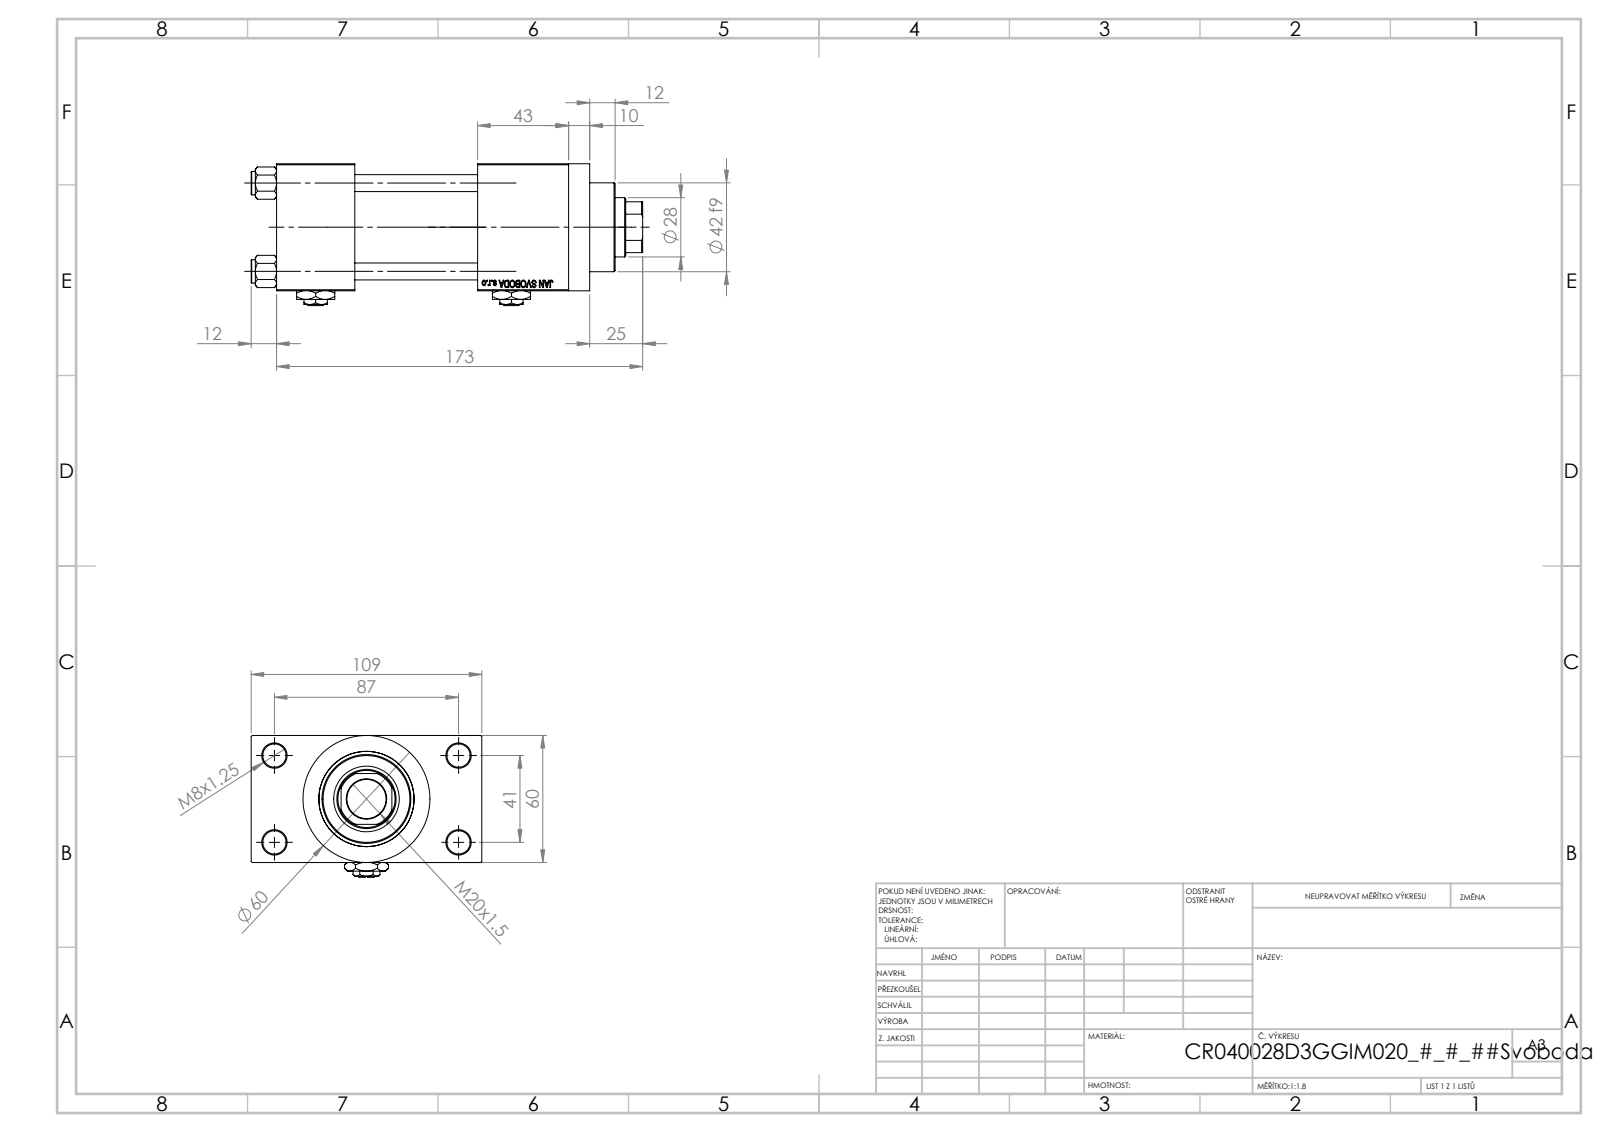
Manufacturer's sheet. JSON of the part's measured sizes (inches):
{"part_name": "V215CR_D_TYCINKA; V215_VC_A; V215CR_D_Body; NUT_M5_D (+2 more)", "step_written_by": "SolidWorks 2019 (CONFIG_CONTROL_DESIGN)", "units": "inches", "bodies": {"solids": 13, "faces": 1206, "planar": 546, "cylindrical": 100, "other": 560}, "overall_size": [7.283, 4.291, 2.638], "volume_in3": 32.46, "surface_area_in2": 202.2, "round_holes": [[0.315, 4], [0.433, 4], [0.276, 2], [0.656, 2], [0.945, 2], [0.728, 1], [1.102, 1], [1.22, 1], [1.575, 1], [1.772, 1]], "round_bosses_or_shafts": [[0.433, 4], [2.362, 1], [1.811, 1], [1.654, 1]], "partial_cylinders_radius": [[0.531, 1]], "face_to_face_distances": [2.362, 3.327, 0.965, 2.283, 1.457, 3.74, 5.433, 3.976, 1.693, 4.291], "hole_center_spacings": [0.892, 1.161, 1.642, 1.856, 1.893, 2.533, 3.011, 1.614]}
